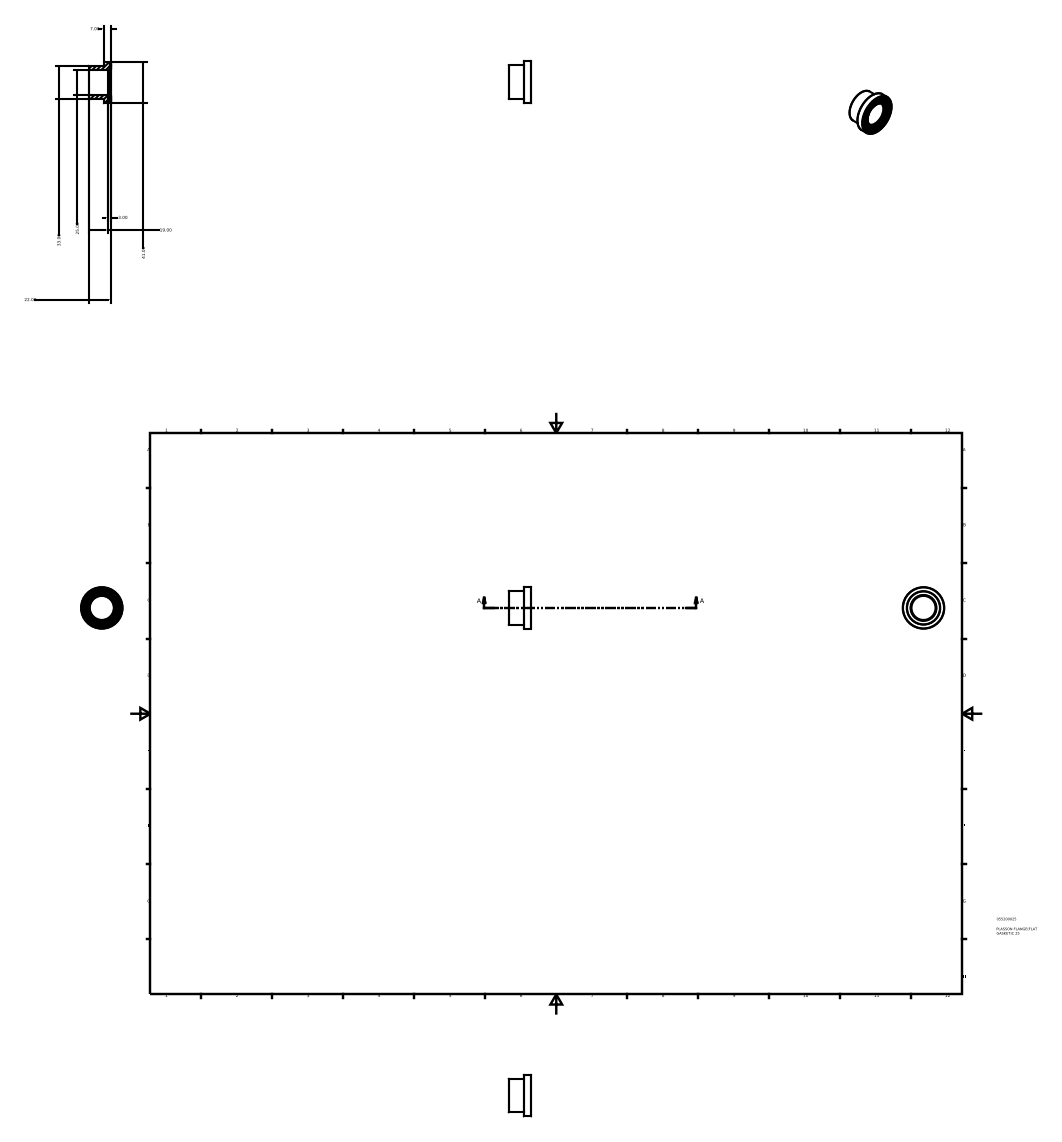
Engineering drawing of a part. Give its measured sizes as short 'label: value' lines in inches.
name: 055200025
written by: Autodesk Inventor 2015 (AUTOMOTIVE_DESIGN)
unit: in
bodies: 1 solid, 33 faces (9 planar, 9 cylindrical, 15 other)
size: 1.614 × 1.614 × 0.866
volume: 0.669 in³; area: 9.639 in²
holes: 1× ⌀0.935, 1× ⌀0.984, 1× ⌀1.048, 1× ⌀1.275, 1× ⌀1.501
bosses: 1× ⌀1.614, 1× ⌀1.388, 1× ⌀1.299, 1× ⌀1.161
face distances: 0.591, 0.866, 0.276, 0.825, 0.234, 0.041, 0.748, 0.157, 0.077, 0.118
